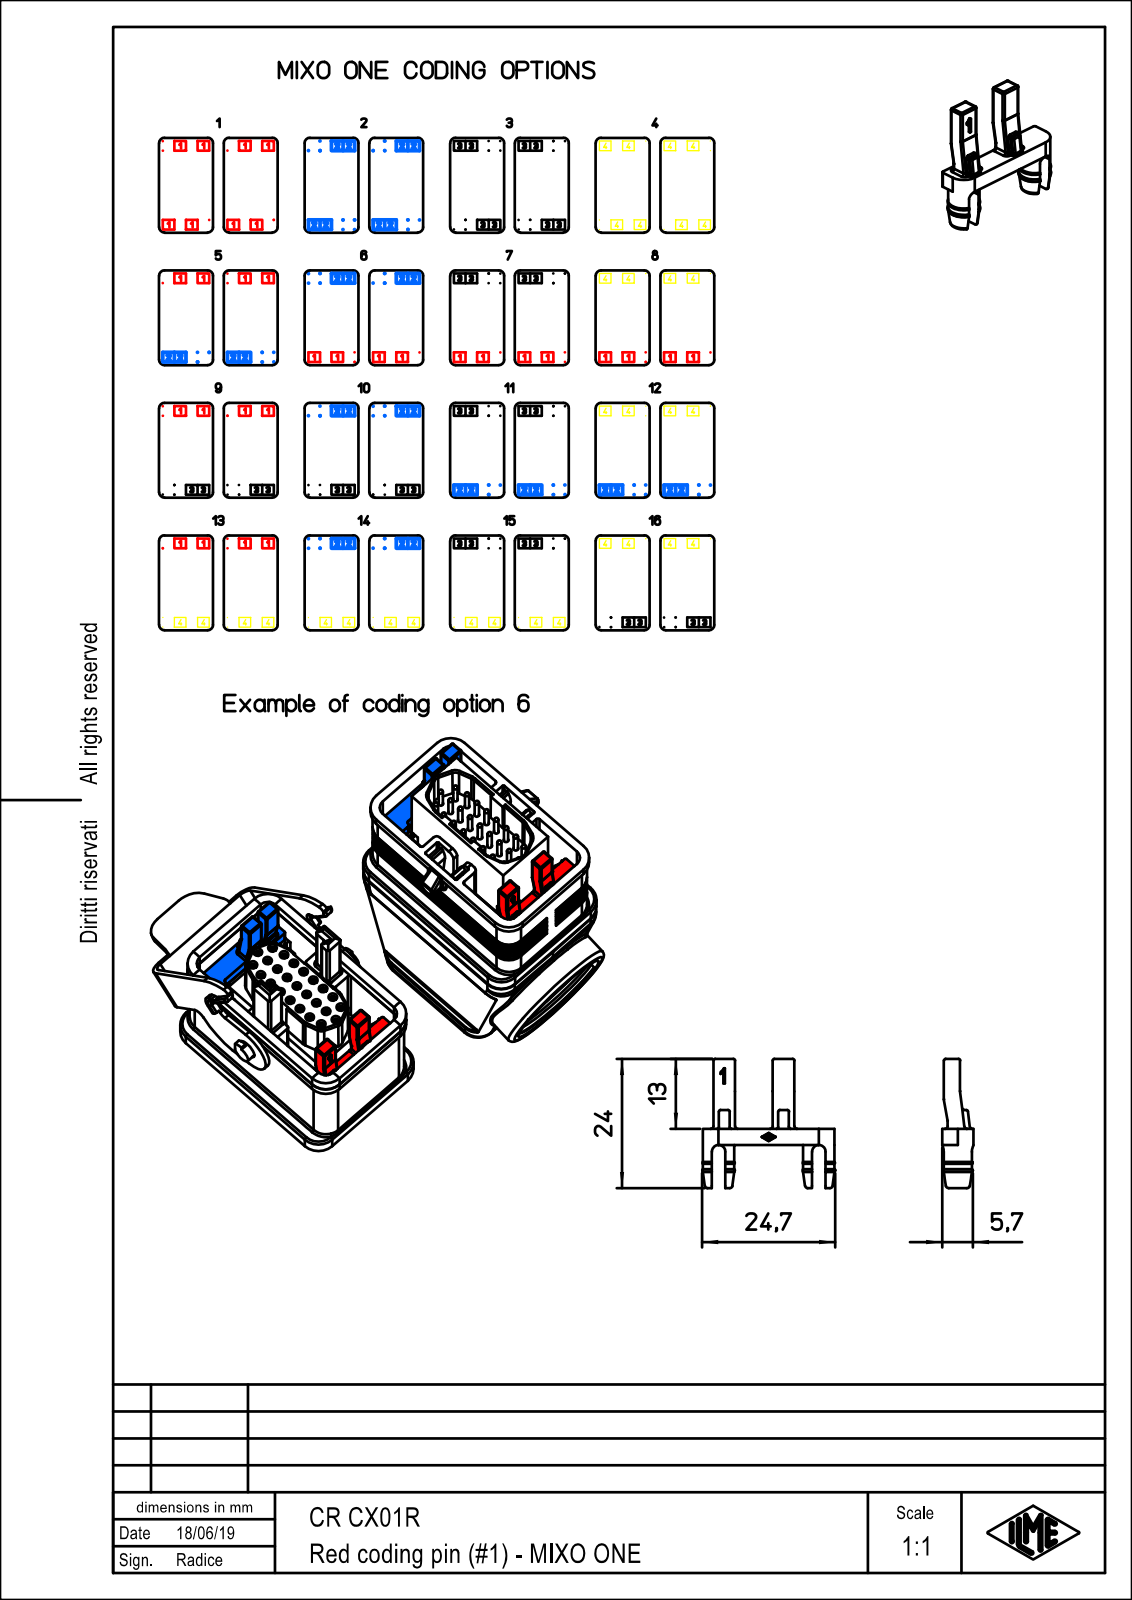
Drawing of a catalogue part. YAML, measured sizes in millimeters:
part_name: "CR_CX01R"
step_written_by: "Creo Elements/Direct Modeling 20.1B 02-Apr-2019 (C) Parametric Technology GmbH (AUTOMOTIVE_DESIGN)"
units: millimeters
bodies: {solids: 1, faces: 49, planar: 35, cylindrical: 10, other: 4}
overall_size: [24.4, 24, 5.8]
volume: 878
surface_area: 1139
round_bosses_or_shafts:
  - {diameter: 5.8, count: 2}
partial_cylinders:
  - {radius: 1.25, count: 2}
face_to_face_distances: [3, 2.5, 11, 4, 18.6, 5.8, 3.3, 5.5, 0.7, 4.8]
